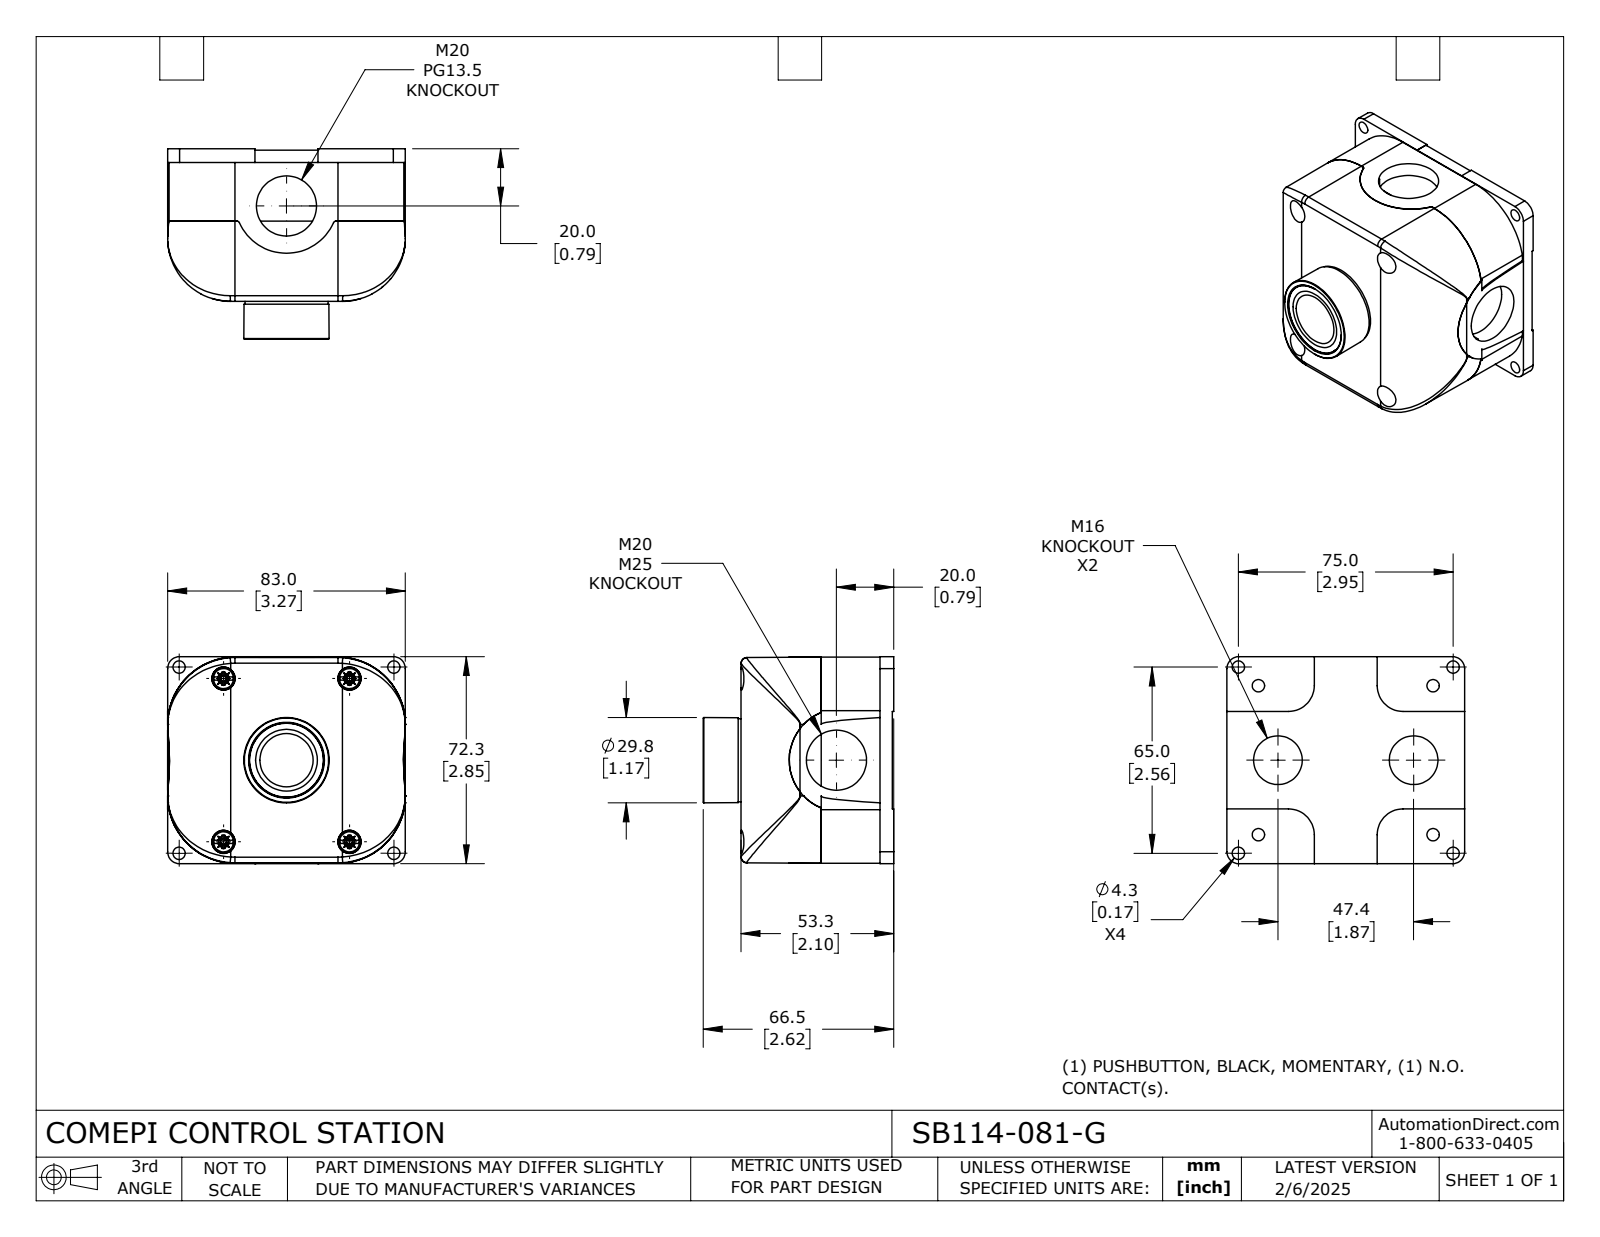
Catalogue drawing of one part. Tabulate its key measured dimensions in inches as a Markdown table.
| quantity | value |
| --- | --- |
| part name | SB114-081-G |
| STEP written by | SolidWorks 2024 (CONFIG_CONTROL_DESIGN) |
| units | inches |
| bodies | 4 solids, 548 faces (300 planar, 144 cylindrical, 104 other) |
| overall size | 3.268 × 2.846 × 2.618 |
| volume | 12.8 in³ |
| surface area | 89.33 in² |
| round holes (diameter × count) | 0.169 × 8, 0.323 × 4, 0.669 × 2, 0.827 × 2, 0.531 × 1, 0.713 × 1, 0.854 × 1 |
| round bosses / shafts (diameter × count) | 0.276 × 4, 1.142 × 1, 1.016 × 1, 0.748 × 1, 0.728 × 1, 0.63 × 1, 0.614 × 1, 0.61 × 1 |
| partial cylindrical surfaces (radius × count) | 0.035 × 4, 0.079 × 4, 0.354 × 4, 0.38 × 4, 0.925 × 4, 0.008 × 2, 0.01 × 2, 0.709 × 2 |
| main face-to-face distances | 0.976, 0.098, 0.878, 2.079, 1.98, 1.102, 0.118, 2.098, 0.02, 0.996 |
| hole center spacings | 0.376, 1.058, 1.39, 1.578, 1.954, 2.32, 2.367, 2.689 |
